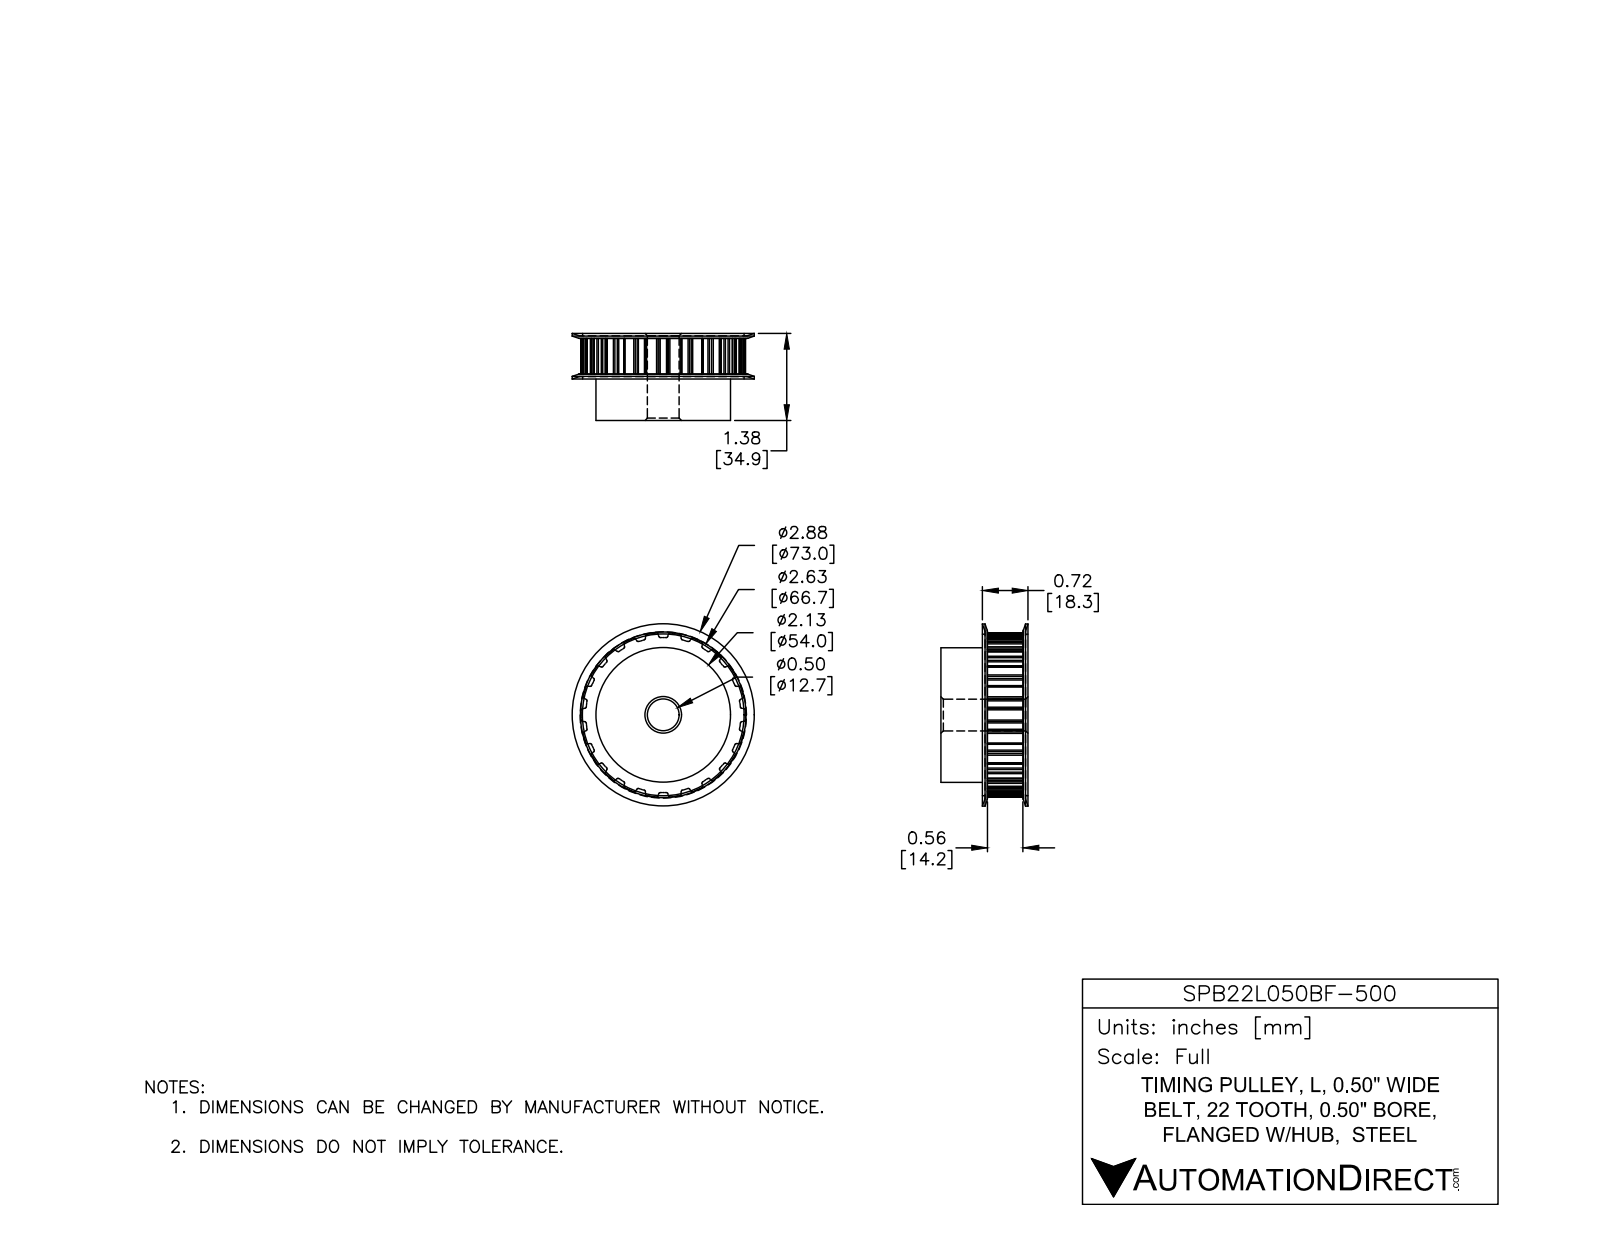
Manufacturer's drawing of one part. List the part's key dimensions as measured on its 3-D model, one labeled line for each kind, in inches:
Part name (STEP PRODUCT): SPB22L050BF-500
STEP written by: SolidWorks 2015 (AUTOMOTIVE_DESIGN)
Units: inches
Bodies: 1 solid, 168 faces (72 planar, 80 cylindrical, 16 other)
Overall size (bounding box): 2.875 × 2.875 × 1.375
Volume: 5.761 in³ · Surface area: 28.62 in²
Round holes (diameter × count): ⌀0.5 ×1
Round bosses / shafts (diameter × count): ⌀2.125 ×1
Partial cylindrical surfaces — rounded edges, fillets, slot ends (radius × count): R0.015 ×44, R1.243 ×1
Main face-to-face distances: 1.375, 0.71, 0.665, 0.04, 0.67, 1.335, 2.596, 0.04, 0.63, 0.08
